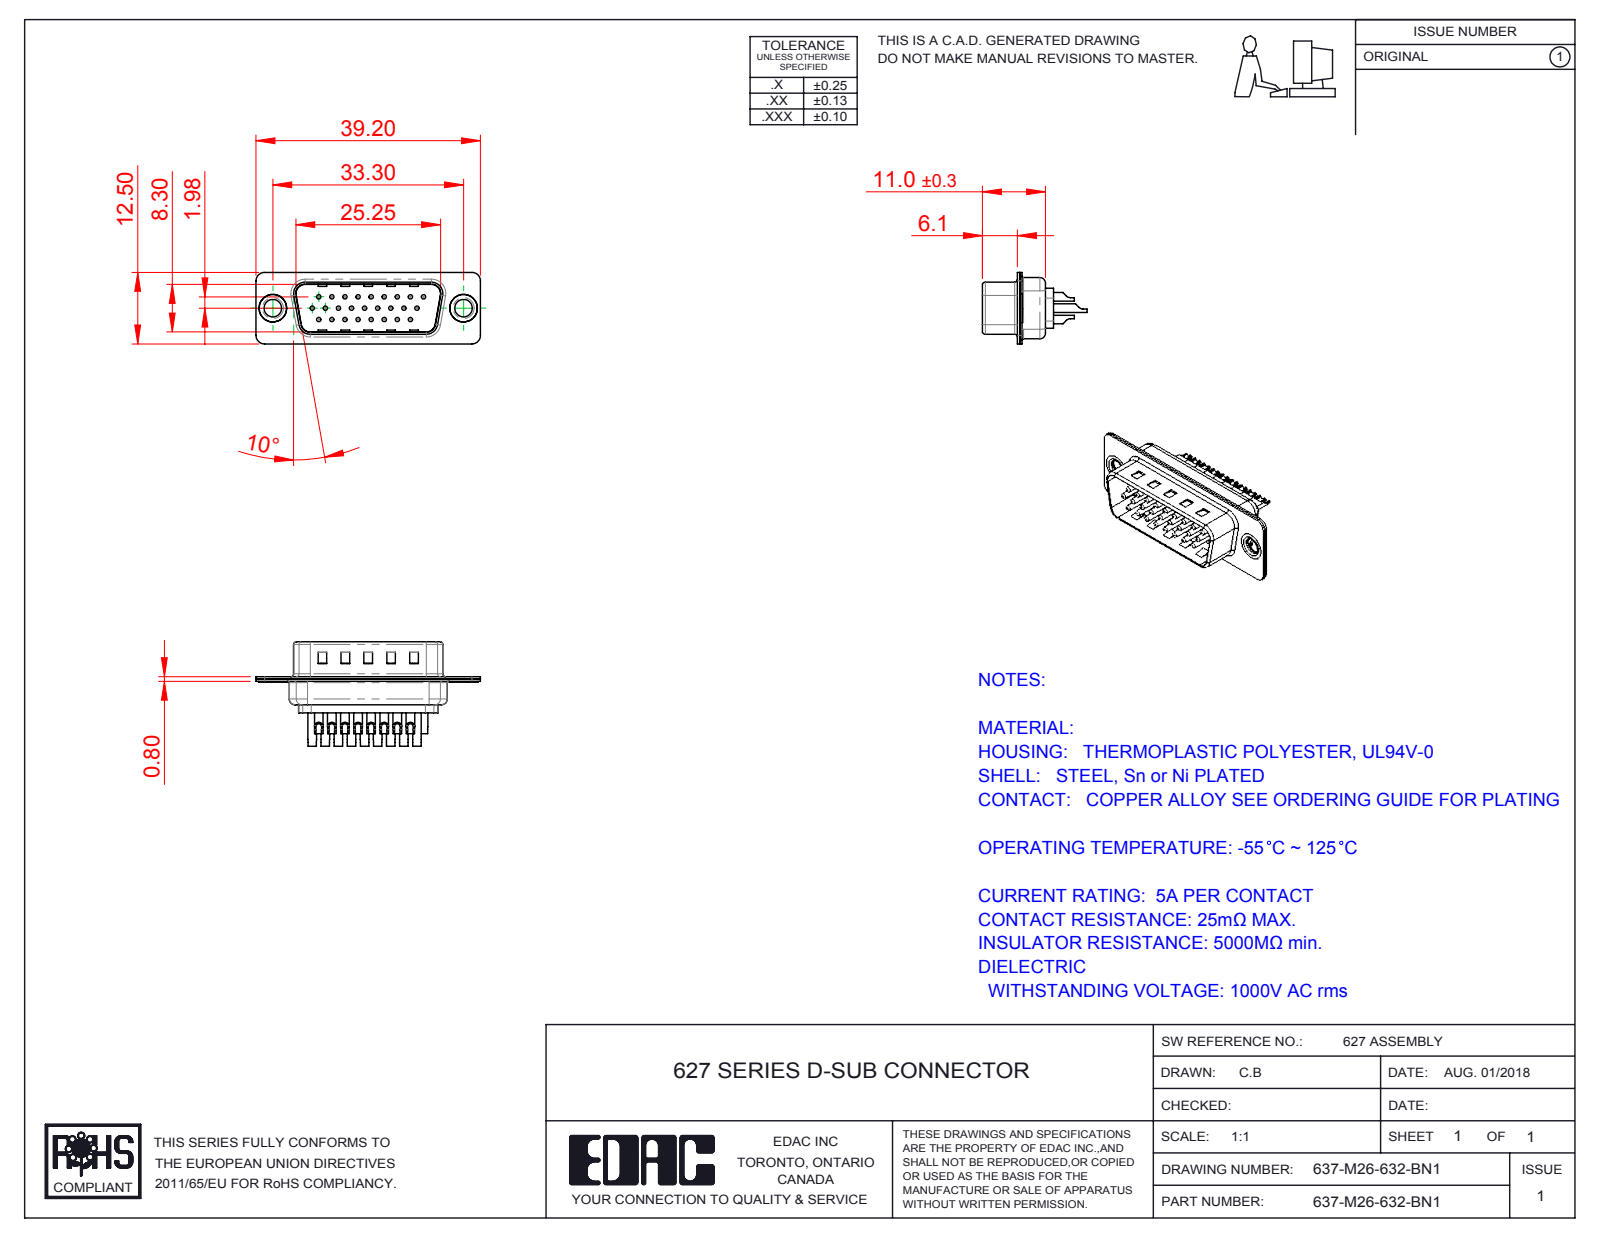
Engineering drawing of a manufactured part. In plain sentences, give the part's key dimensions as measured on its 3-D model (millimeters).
The part is named "637M Contact Row 3_32; 637M Thru Hole Rivet; 637M Shell Front_26 Contacts; 637-M26-632-BN1 (+4 more)". Its 3-D file was written by "SolidWorks 2016 (CONFIG_CONTROL_DESIGN)". It is 31 solids with 1276 faces: 373 planar, 533 cylindrical and 370 other. Overall it measures 39.2 by 18.25 by 12.5 millimeters. Its volume is 1 918 cubic millimeters and its surface area 5 928 square millimeters. Round holes: 26 of diameter 0.75, 26 of diameter 1, 26 of diameter 1.6, 26 of diameter 2, 2 of diameter 3.05, 2 of diameter 4, 2 of diameter 4.8. Round bosses or shafts: 26 of diameter 1.5, 2 of diameter 5, 2 of diameter 4.9, 2 of diameter 3.55. Partial cylindrical surfaces (rounded edges, fillets, slot ends): 16 of radius 1.5, 12 of radius 2, 8 of radius 0.5, 8 of radius 1.6, 7 of radius 1, 4 of radius 0.25, 4 of radius 0.6, 4 of radius 0.65. The main face-to-face distances are 0.4, 0.8, 9.5, 9.1, 8.7, 9.9, 0.75, 0.35, 1.2, 1.1. The hole center spacings are 3.96, 2.28, 4.57, 6.05, 2.29, 8.24, 6.86, 10.48.
